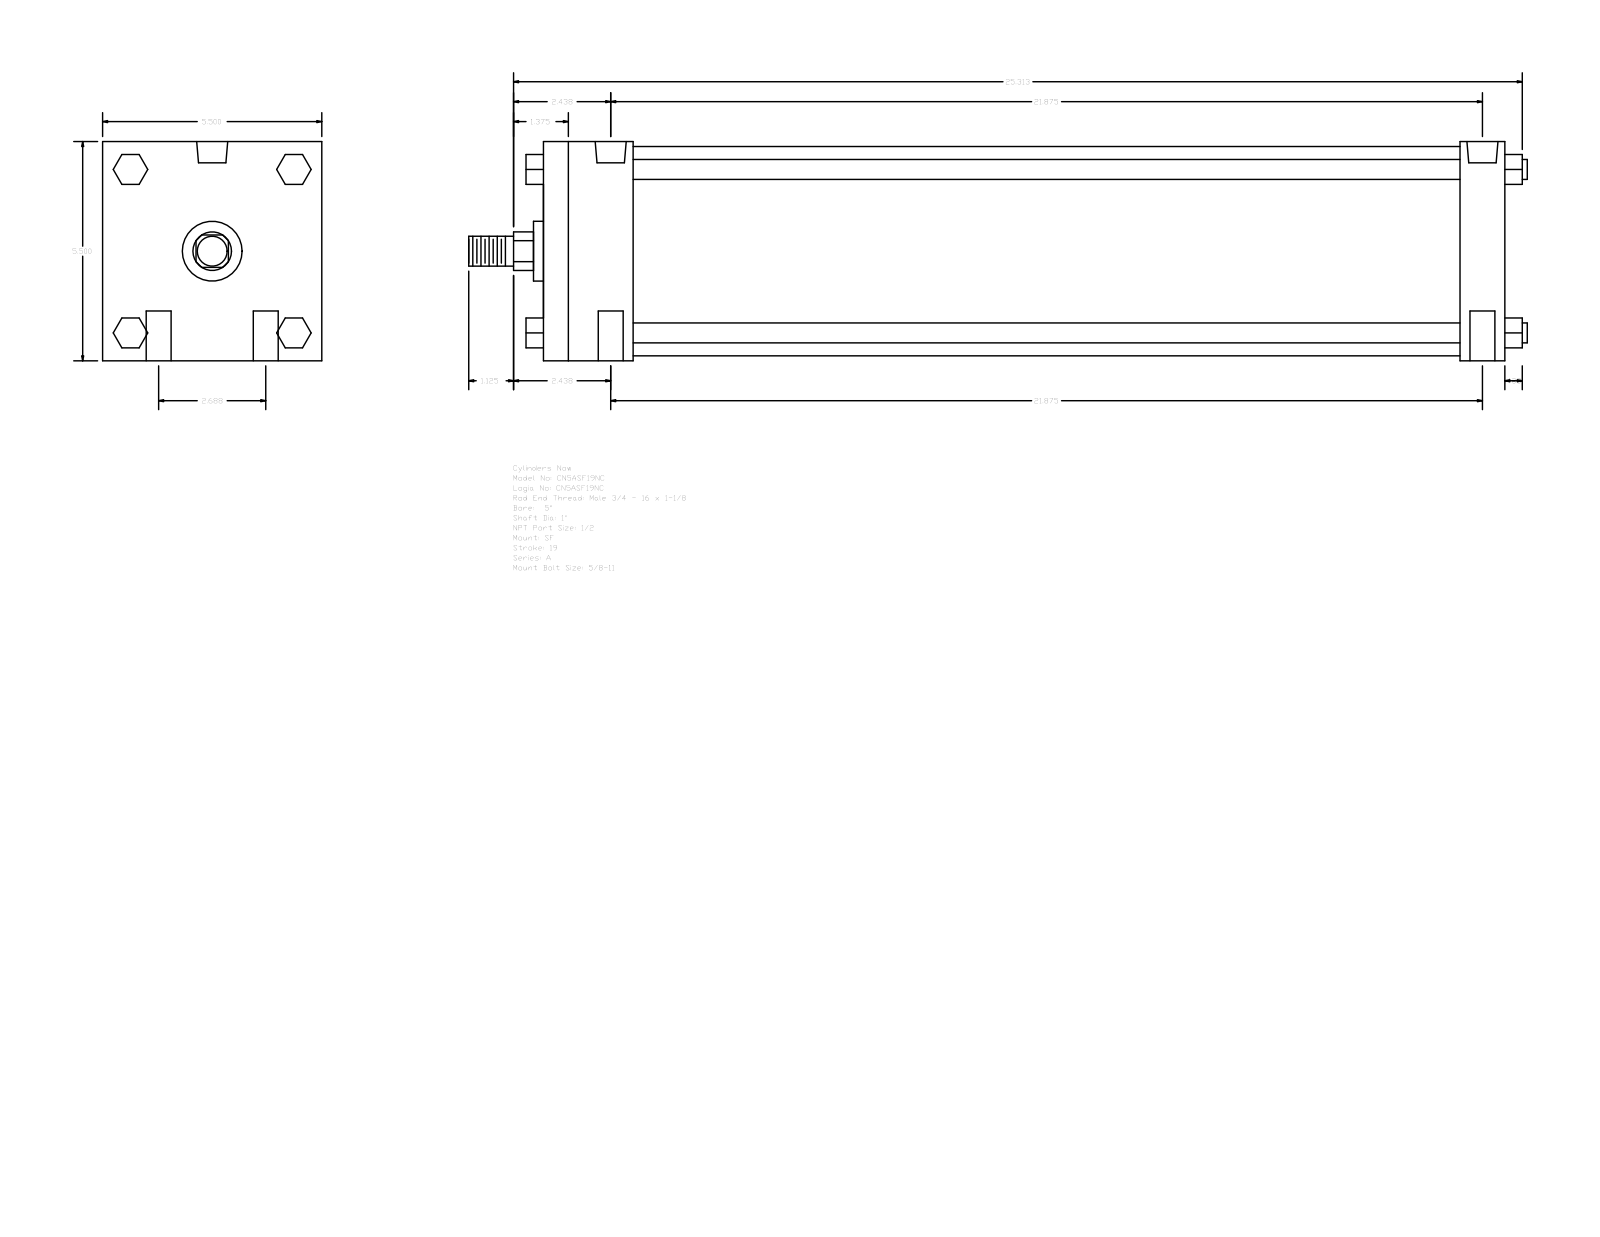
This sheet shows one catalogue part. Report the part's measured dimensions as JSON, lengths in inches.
{"part_name": "A_SF__0500_1", "step_written_by": "GSSL Pune (CONFIG_CONTROL_DESIGN)", "units": "inches", "bodies": {"solids": 0, "faces": 124, "planar": 94, "cylindrical": 30, "other": 0}, "overall_size": [26.563, 5.5, 5.5], "round_holes": [[0.625, 4], [0.344, 2], [0.778, 2]], "round_bosses_or_shafts": [[0.5, 4], [5.25, 1], [1.5, 1], [1, 1], [0.75, 1]], "partial_cylinders_radius": [[0.484, 1]], "face_to_face_distances": [5.5, 24.125, 2.25, 23, 20.75, 21.875, 1.125, 0.75, 2.05, 3.55], "hole_center_spacings": [1.344, 21.917, 21.875, 2.687, 22.04, 21.687]}
